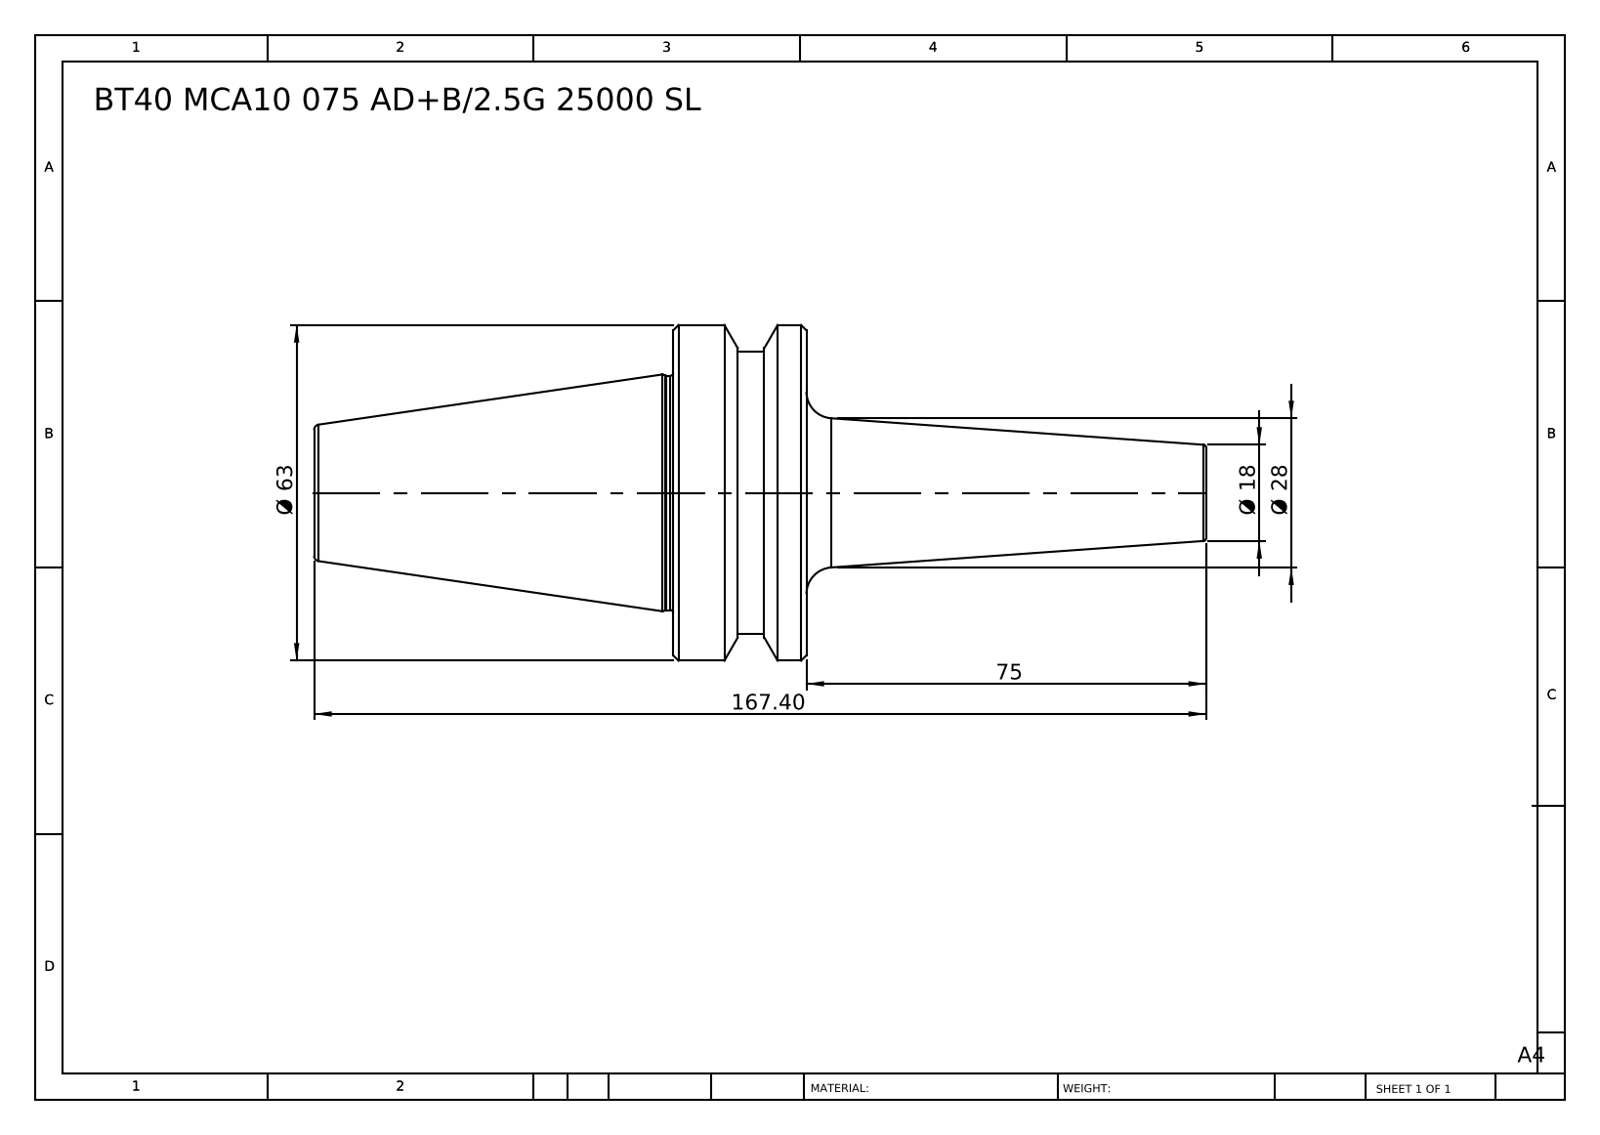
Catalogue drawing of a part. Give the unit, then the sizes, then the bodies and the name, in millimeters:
Units: millimetres
Overall size (bounding box): 167.4 × 63 × 63
Round bosses / shafts (diameter × count): ⌀63 ×1, ⌀53 ×1, ⌀44 ×1
Main face-to-face distances: 25, 92.4, 67.4, 75, 100, 167.4, 87.9, 12.9, 12.1, 79.5
Volume: 171 400 mm³ · Surface area: 23 289 mm²
Bodies: 1 solid, 38 faces (6 planar, 8 cylindrical, 24 other)
Part name (STEP PRODUCT): BT40 MCA10 075 AD+B-2.5G 25000 SL
STEP written by: SolidWorks 2014 (CONFIG_CONTROL_DESIGN)
